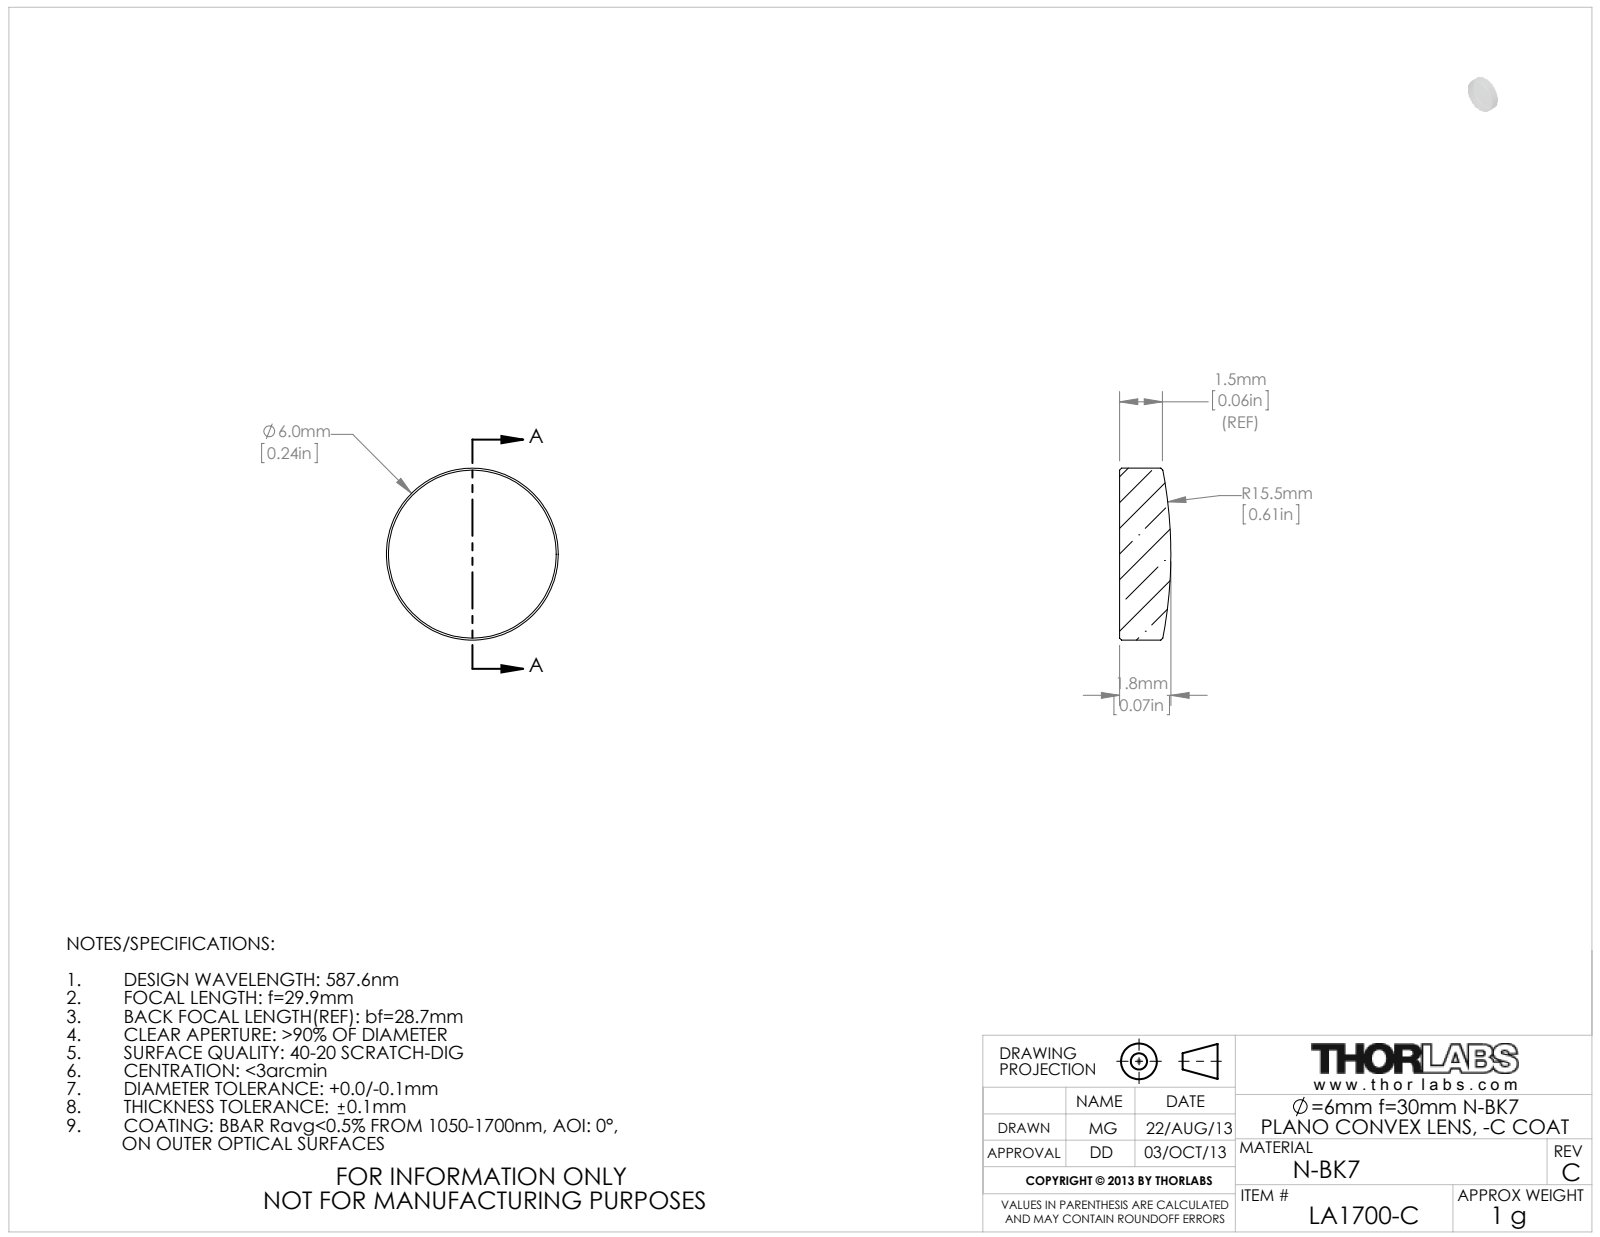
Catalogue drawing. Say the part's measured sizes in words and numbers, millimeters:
The part is named "4565-E0W". Its 3-D file was written by "SolidWorks 2009 (AUTOMOTIVE_DESIGN)". It is 1 solid with 5 faces: 1 planar, 2 cylindrical and 2 other. Overall it measures 6 by 6 by 1.79 millimeters. Its volume is 46 cubic millimeters and its surface area 85 square millimeters. Round bosses or shafts: 1 of diameter 6.
